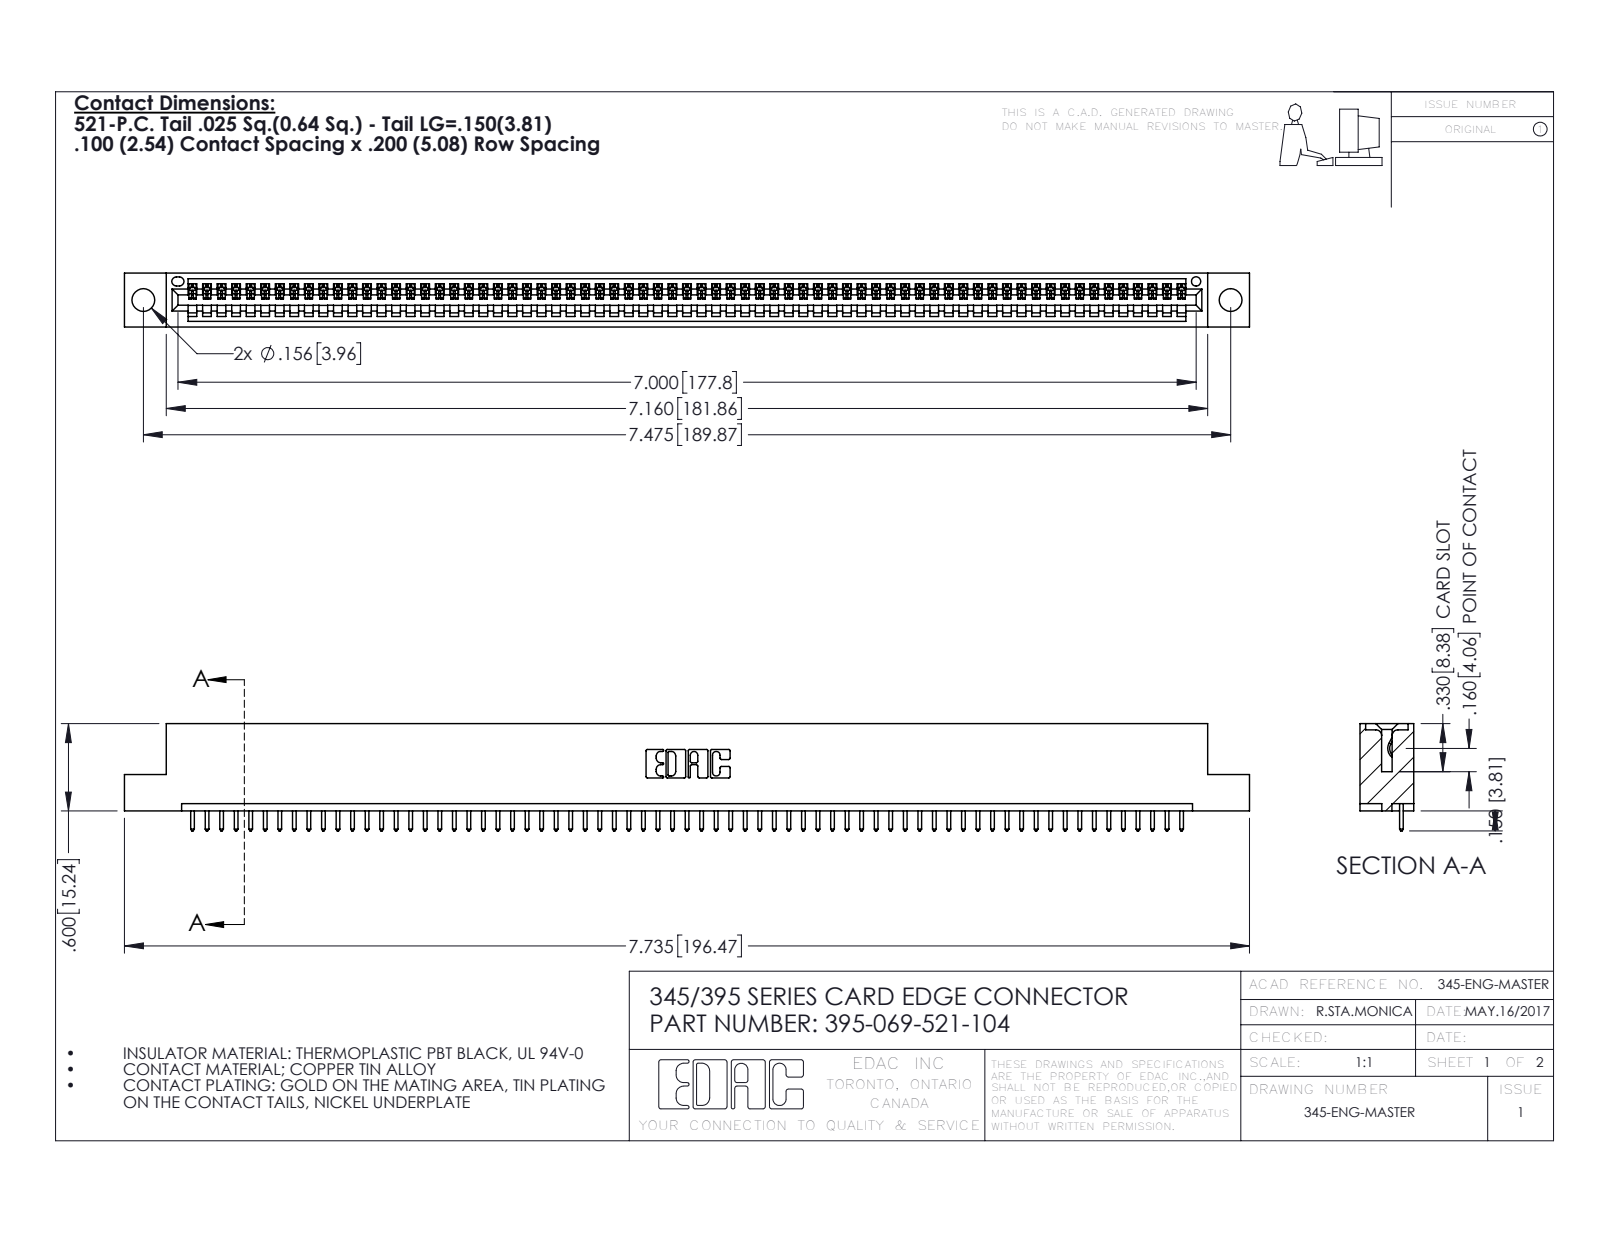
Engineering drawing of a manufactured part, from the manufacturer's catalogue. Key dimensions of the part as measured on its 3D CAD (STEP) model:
Part name (STEP PRODUCT): 395-069-521-104; 345-292-001_345-293-121; 345 Part_Flush Mounting Lugs - 0.156 Dia-TH
STEP written by: SolidWorks 2016 (CONFIG_CONTROL_DESIGN)
Units: inches
Bodies: 70 solids, 4128 faces (2840 planar, 1288 cylindrical, 0 other)
Overall size (bounding box): 7.735 × 0.737 × 0.37
Volume: 1.135 in³ · Surface area: 37.39 in²
Round holes (diameter × count): ⌀0.156 ×2, ⌀0.064 ×1
Partial cylindrical surfaces — rounded edges, fillets, slot ends (radius × count): R0.006 ×138, R0.01 ×138, R0.01 ×22, R0.007 ×6, R0.031 ×6, R0.026 ×3, R0.031 ×2, R0.04 ×2
Main face-to-face distances: 0.298, 0.072, 0.37, 0.2, 0.098, 0.272, 0.025, 0.225, 0.149, 0.072
Hole centre spacings: 0.27, 7.239, 7.475
